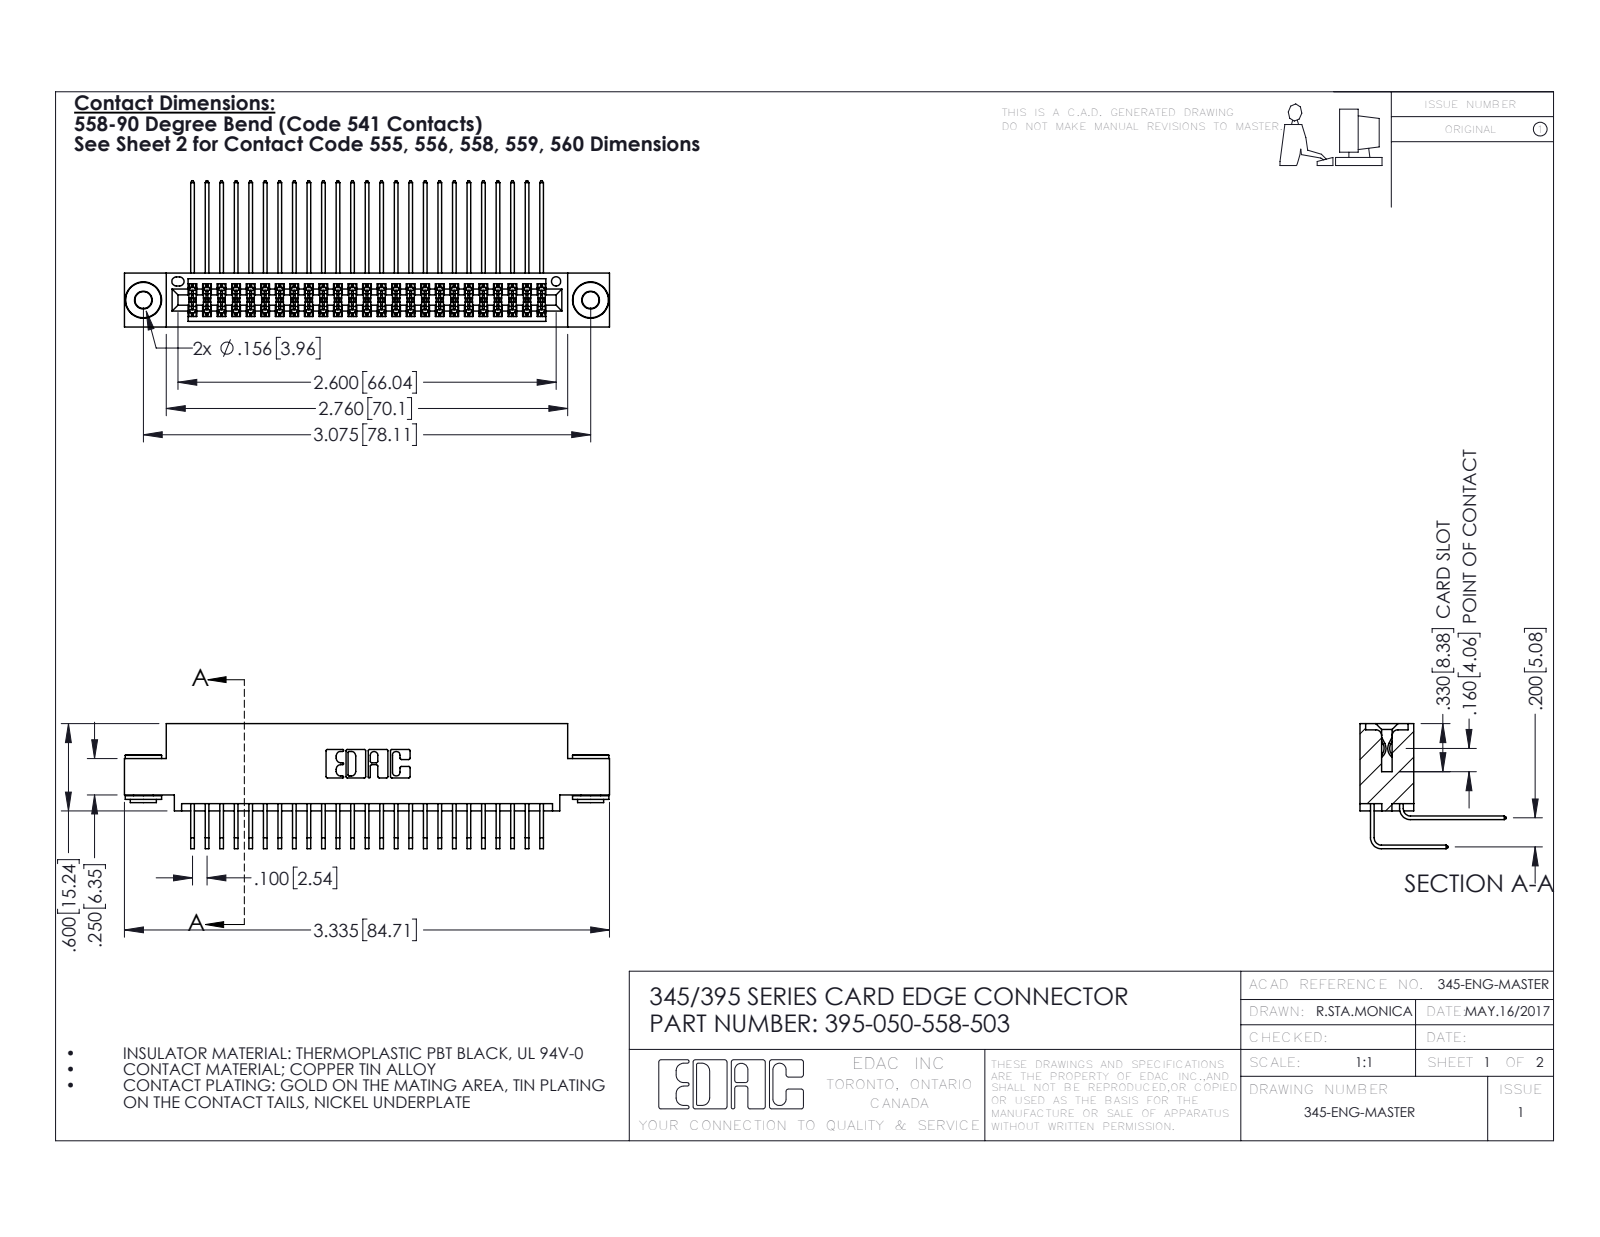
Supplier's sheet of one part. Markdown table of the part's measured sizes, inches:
| quantity | value |
| --- | --- |
| part name | 345 Part_0.110 Offset - 0.156 Dia-TH; 345-250-002_345-250-002-102; 395-050-558-503; 345-292-001_558 Tail - 2 (+1 more) |
| STEP written by | SolidWorks 2016 (CONFIG_CONTROL_DESIGN) |
| units | inches |
| bodies | 53 solids, 2768 faces (1844 planar, 916 cylindrical, 8 other) |
| overall size | 3.335 × 1.005 × 0.859 |
| volume | 0.507 in³ |
| surface area | 21.08 in² |
| round holes (diameter × count) | 0.116 × 2, 0.156 × 2, 0.064 × 1 |
| round bosses / shafts (diameter × count) | 0.25 × 2, 0.18 × 2, 0.136 × 2 |
| partial cylindrical surfaces (radius × count) | 0.006 × 76, 0.01 × 22, 0.007 × 6, 0.031 × 6, 0.026 × 3, 0.014 × 2, 0.019 × 2, 0.022 × 2 |
| main face-to-face distances | 0.072, 0.298, 0.2, 0.37, 0.025, 0.098, 0.272, 0.225, 0.025, 0.175 |
| hole center spacings | 0.27, 2.84, 3.075 |
